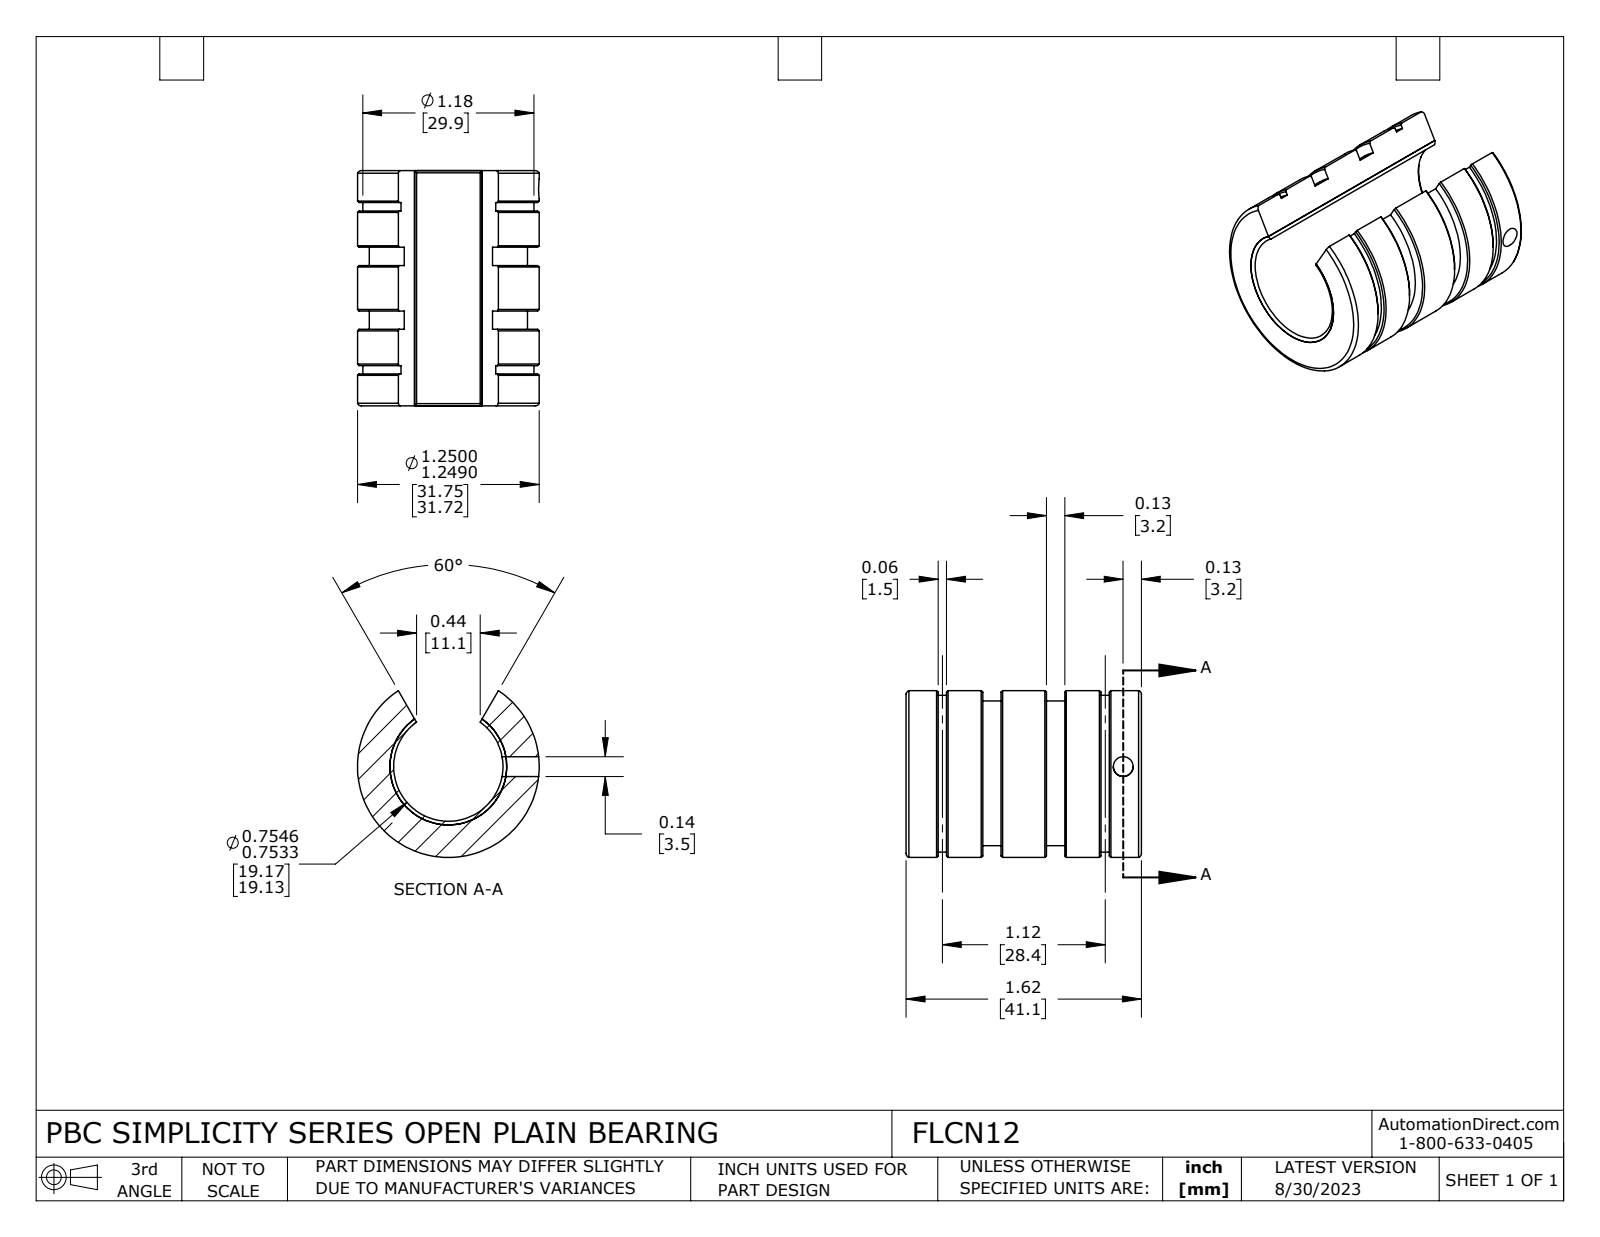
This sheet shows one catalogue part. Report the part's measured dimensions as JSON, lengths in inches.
{"part_name": "FLCN12", "step_written_by": "SolidWorks 2021 (CONFIG_CONTROL_DESIGN)", "units": "inches", "bodies": {"solids": 2, "faces": 82, "planar": 14, "cylindrical": 40, "other": 28}, "overall_size": [1.618, 1.249, 1.146], "volume_in3": 0.945, "surface_area_in2": 17.88, "round_holes": [[0.136, 1], [0.751, 1], [0.802, 1]], "round_bosses_or_shafts": [[1.249, 1], [1.177, 1], [1.087, 1]], "face_to_face_distances": [1.617, 0.527, 1.091, 0.653, 0.965, 0.126, 0.438, 0.312, 0.564, 0.22]}
